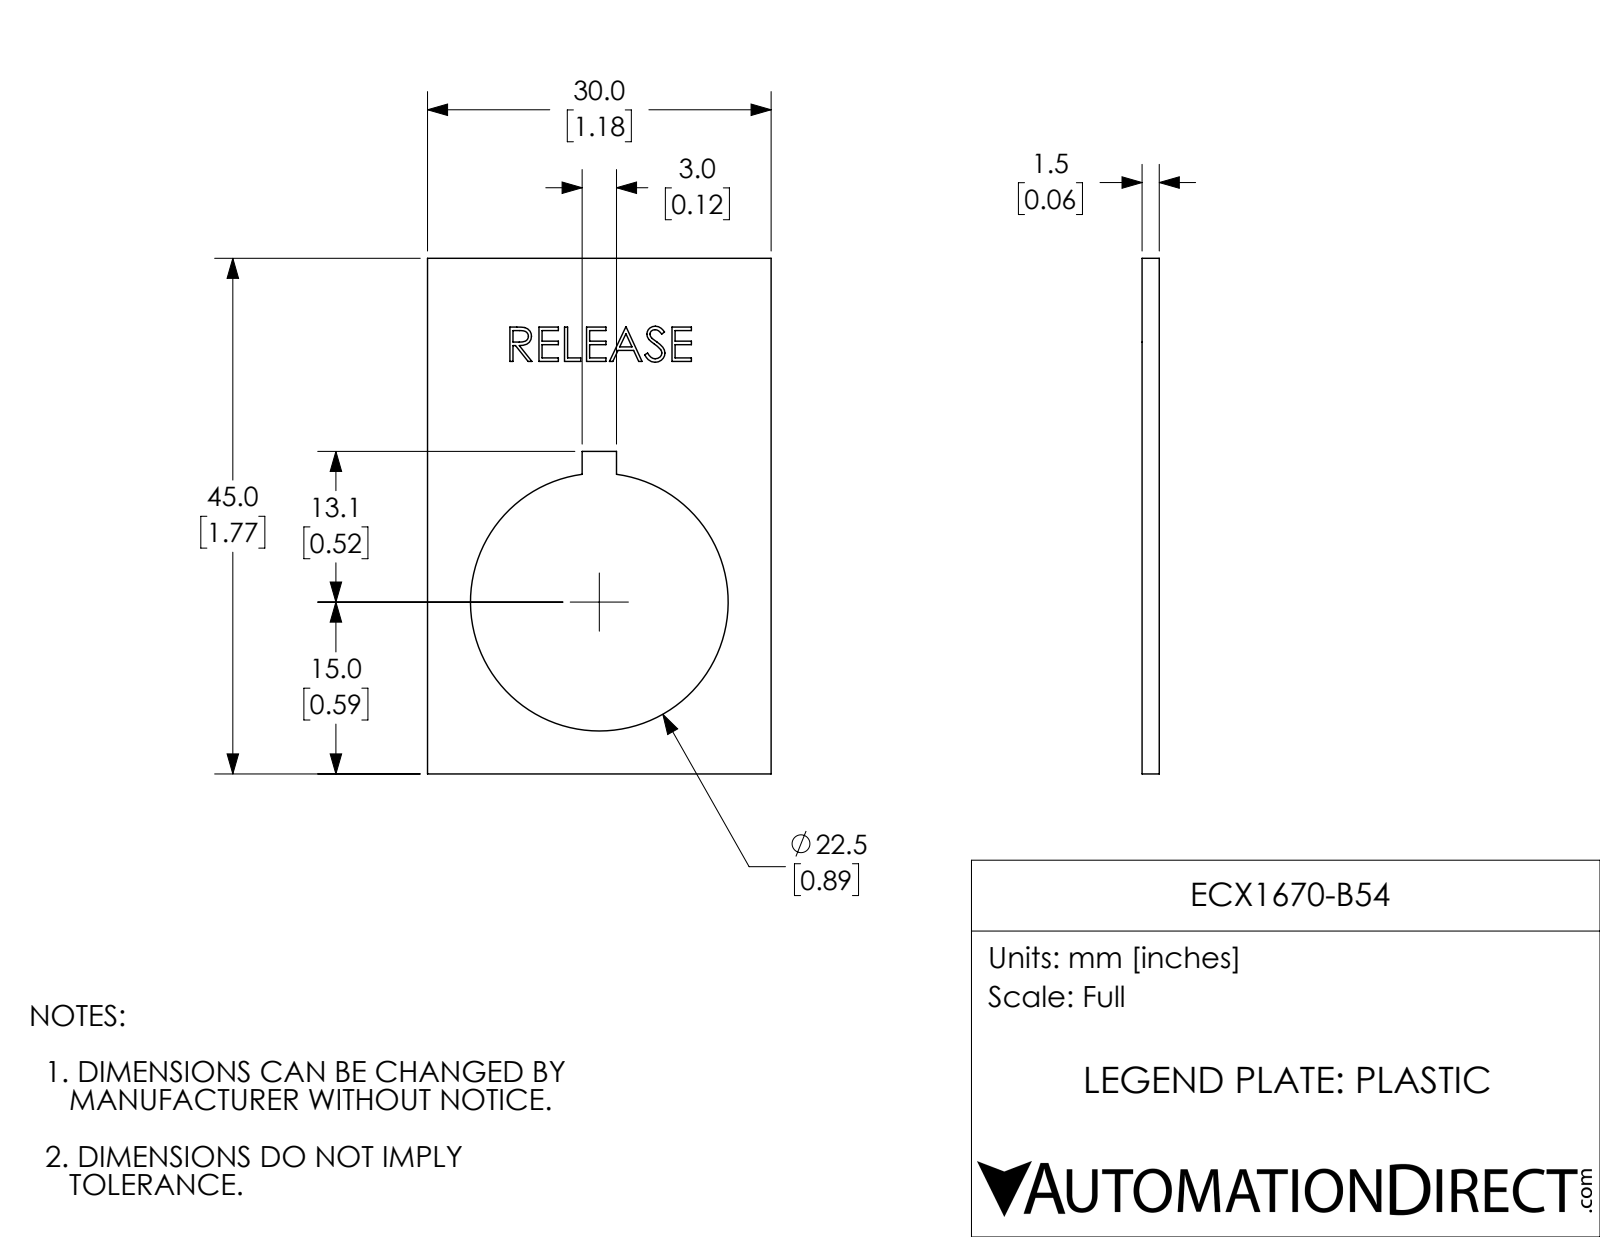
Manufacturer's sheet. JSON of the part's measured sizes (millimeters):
{"part_name": "ECX1670-B54", "step_written_by": "SolidWorks 2017 (AUTOMOTIVE_DESIGN)", "units": "millimeters", "bodies": {"solids": 1, "faces": 107, "planar": 84, "cylindrical": 3, "other": 20}, "overall_size": [45, 30, 1.5], "volume_mm3": 1400, "surface_area_mm2": 2233, "round_holes": [[22.5, 1]], "face_to_face_distances": [1.5, 30, 45, 1.5, 13.5, 16.5, 28.1, 16.8, 3, 0.3]}
